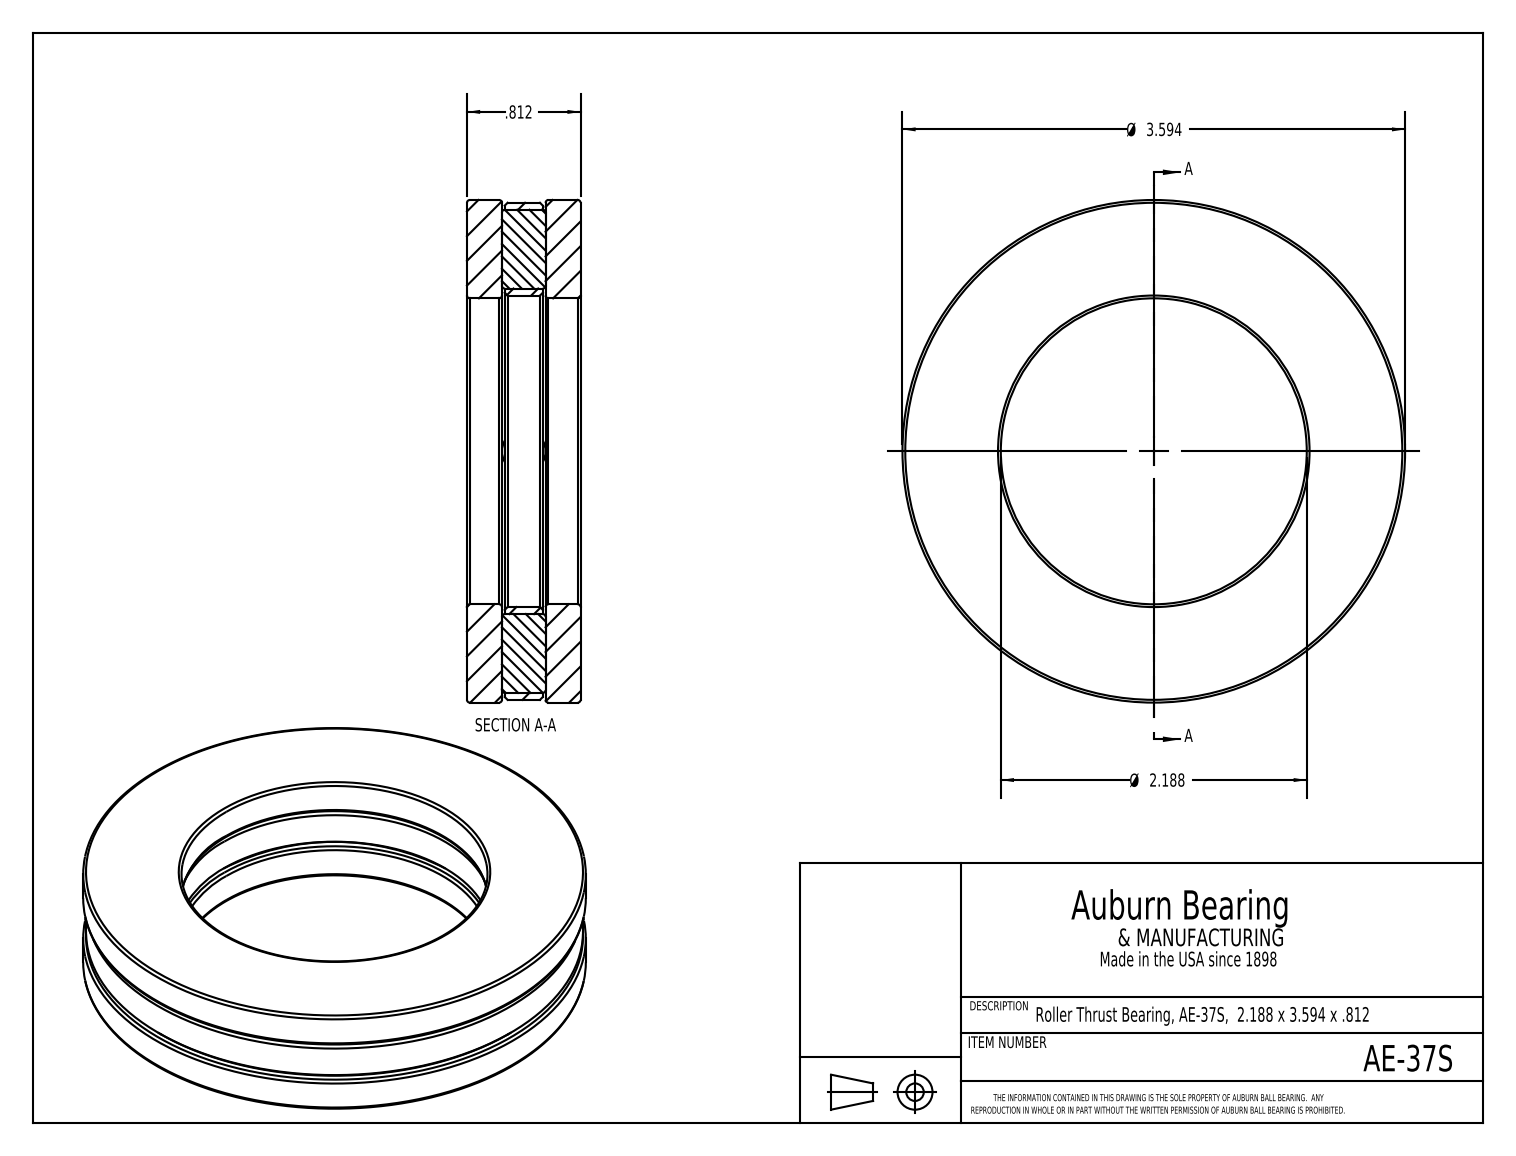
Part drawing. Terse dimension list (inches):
name: AE-37S
written by: SolidWorks 2017 (CONFIG_CONTROL_DESIGN)
unit: in
bodies: 7 solids, 60 faces (30 planar, 10 cylindrical, 20 other)
size: 3.594 × 3.594 × 0.812
volume: 4.797 in³; area: 53.81 in²
holes: 1× ⌀2.187, 1× ⌀2.227
bosses: 2× ⌀0.312, 1× ⌀3.594, 1× ⌀3.554
face distances: 0.25, 0.562, 0.27, 0.542, 0.02, 0.292, 0.312, 0.812, 0.272, 1.008
